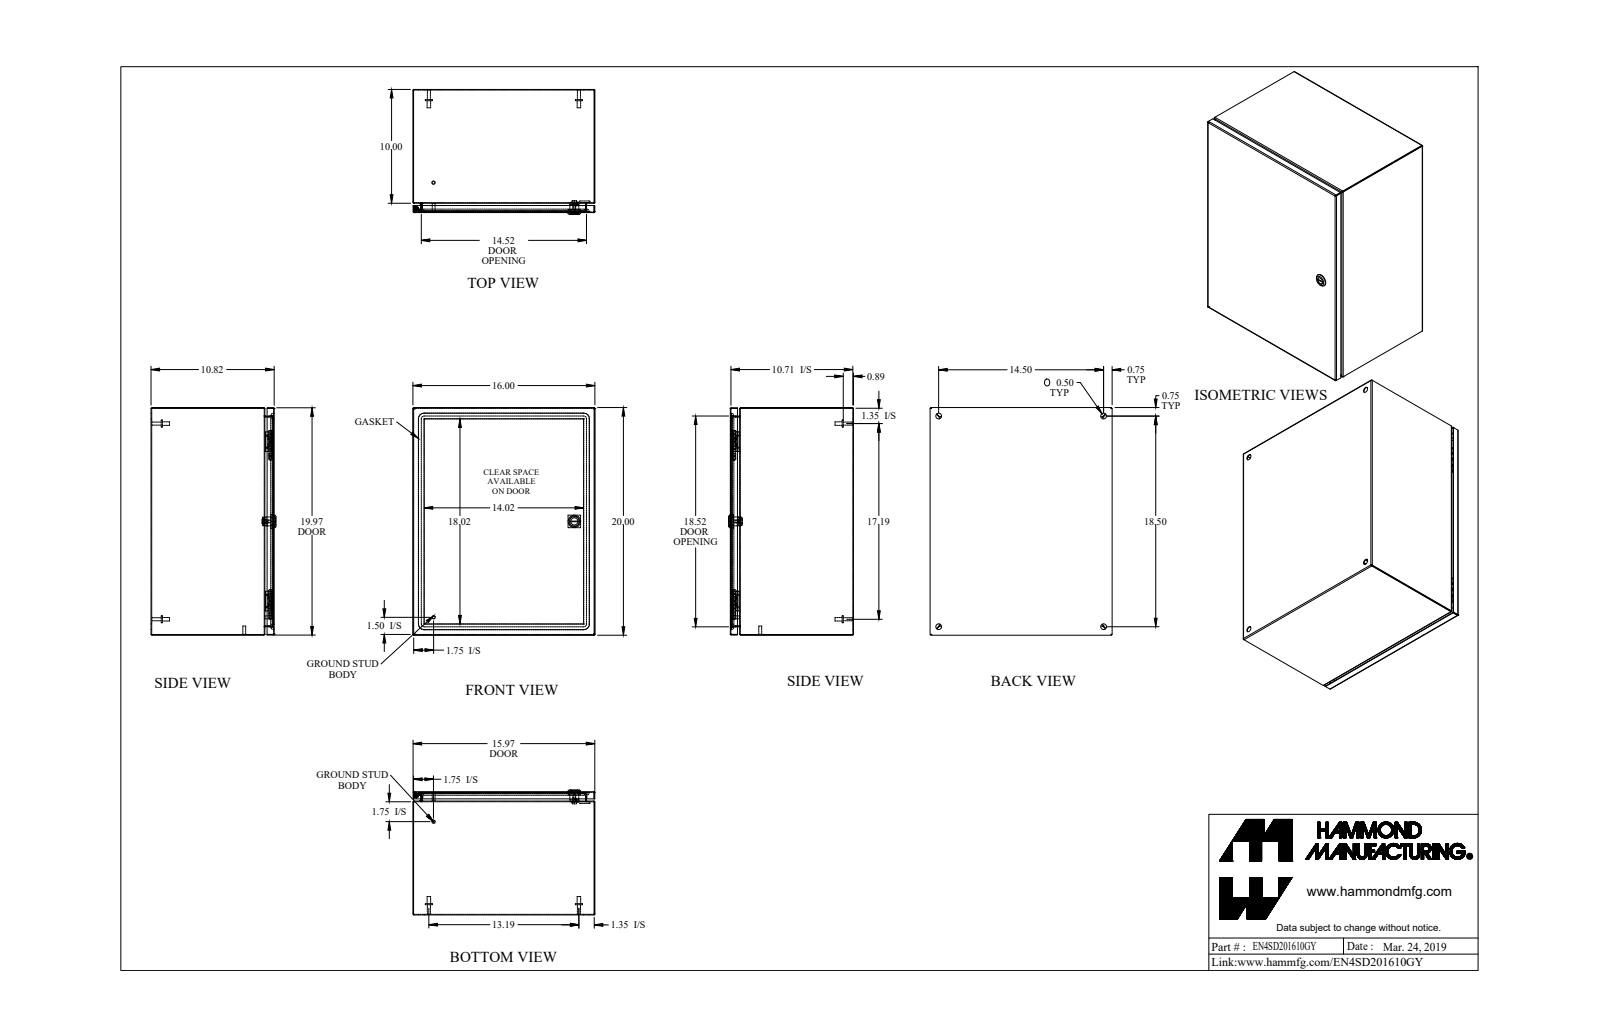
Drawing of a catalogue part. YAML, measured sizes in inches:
part_name: "EN4SD201610GY_Default"
step_written_by: "SolidWorks 2019 (CONFIG_CONTROL_DESIGN)"
units: inches
bodies: {solids: 21, faces: 634, planar: 285, cylindrical: 213, other: 136}
overall_size: [20, 16, 10.982]
volume: 92.6
surface_area: 3159
round_holes:
  - {diameter: 0.5, count: 4}
  - {diameter: 0.172, count: 1}
  - {diameter: 0.232, count: 1}
  - {diameter: 0.24, count: 1}
  - {diameter: 0.242, count: 1}
  - {diameter: 0.625, count: 1}
  - {diameter: 0.785, count: 1}
round_bosses_or_shafts:
  - {diameter: 0.625, count: 4}
  - {diameter: 0.313, count: 4}
  - {diameter: 0.27, count: 4}
  - {diameter: 0.281, count: 2}
  - {diameter: 0.25, count: 2}
  - {diameter: 1.1, count: 1}
  - {diameter: 0.525, count: 1}
  - {diameter: 0.455, count: 1}
partial_cylinders:
  - {radius: 0.029, count: 21}
  - {radius: 0.086, count: 21}
  - {radius: 0.25, count: 16}
  - {radius: 19, count: 8}
  - {radius: 0.006, count: 4}
  - {radius: 0.062, count: 4}
  - {radius: 0.499, count: 4}
  - {radius: 0.125, count: 2}
face_to_face_distances: [0.057, 10.765, 15.943, 10.708, 10.822, 19.943, 15.886, 16, 19.886, 20]
hole_center_spacings: [14.5, 18.5, 23.506, 9.31, 9.311, 16.316, 16.317]
